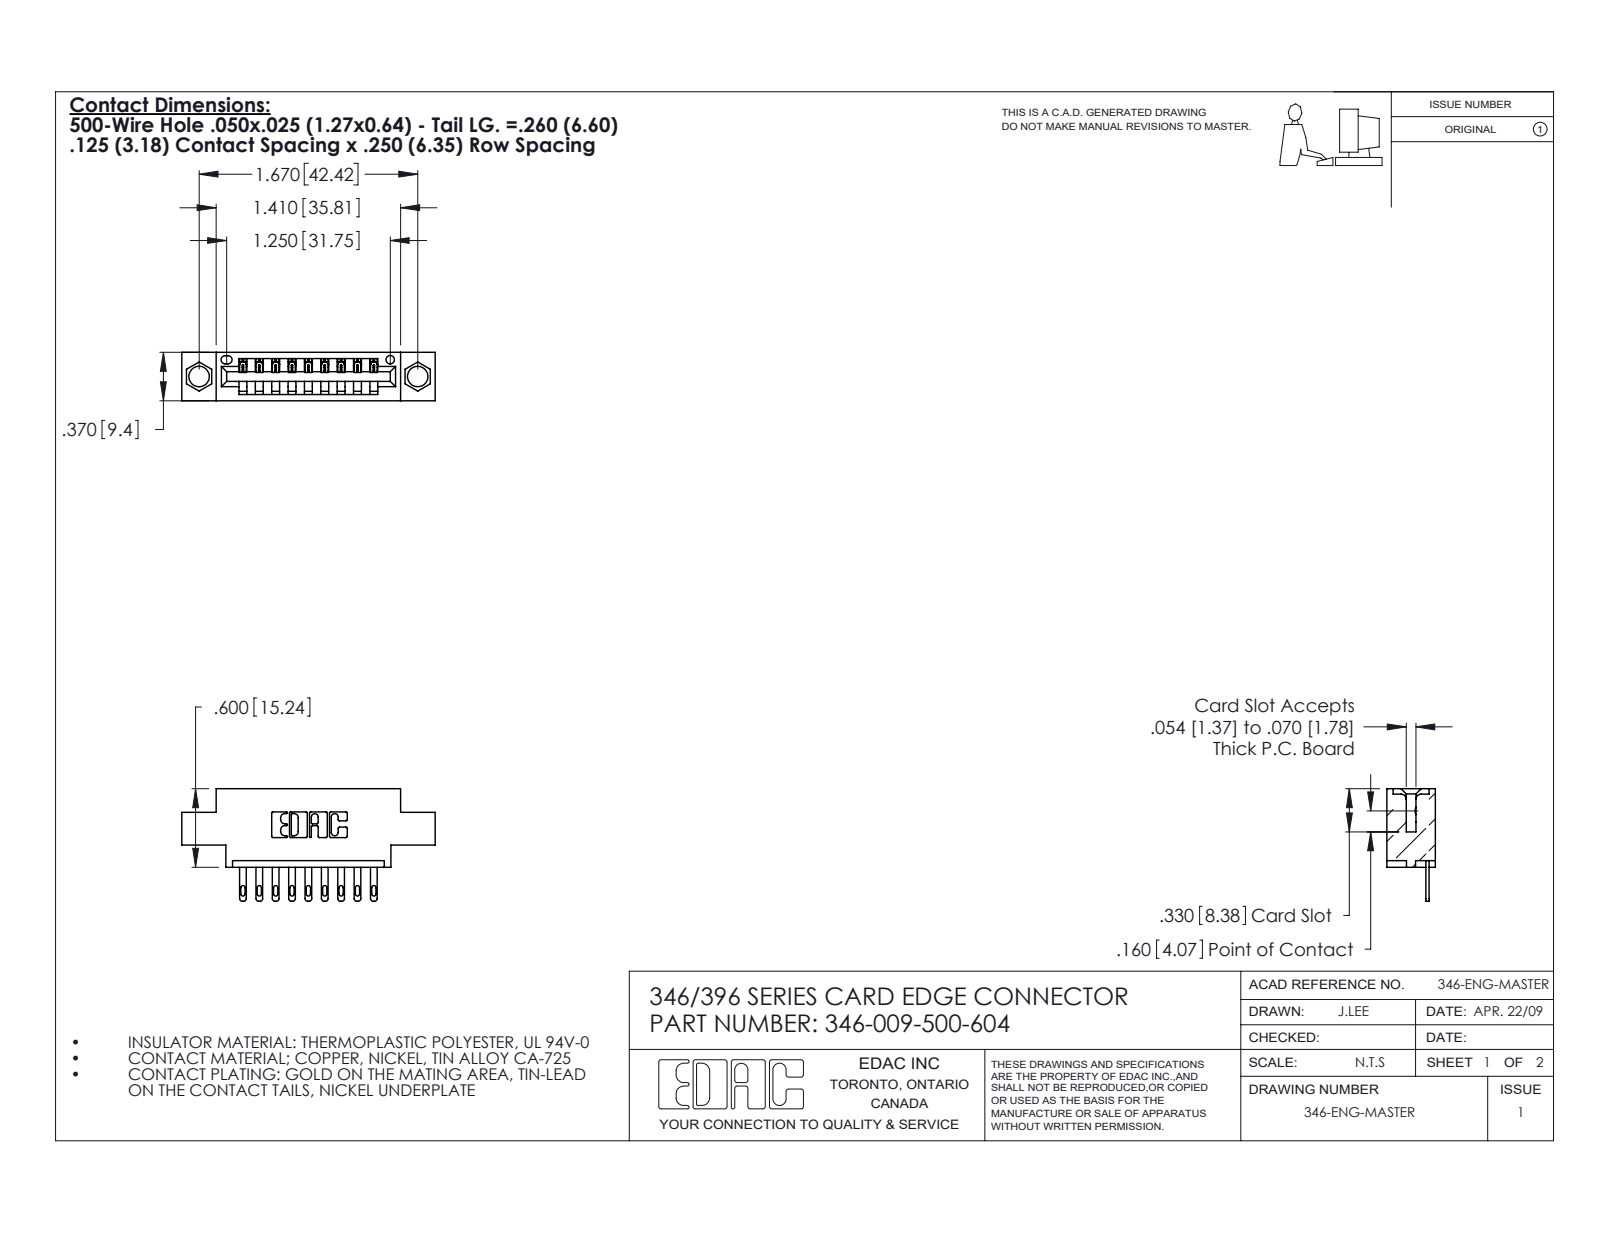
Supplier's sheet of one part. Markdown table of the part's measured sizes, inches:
| quantity | value |
| --- | --- |
| part name | 346-009-500-604; 346 Part_0.170 Offset - 0.156 Dia-TH; 345-292-001_345-293-100 |
| STEP written by | SolidWorks 2020 (CONFIG_CONTROL_DESIGN) |
| units | inches |
| bodies | 10 solids, 626 faces (400 planar, 226 cylindrical, 0 other) |
| overall size | 1.935 × 0.86 × 0.37 |
| volume | 0.258 in³ |
| surface area | 7.657 in² |
| round holes (diameter × count) | 0.156 × 2, 0.064 × 1 |
| partial cylindrical surfaces (radius × count) | 0.01 × 22, 0.006 × 18, 0.016 × 18, 0.02 × 18, 0.007 × 6, 0.031 × 6, 0.026 × 3, 0.031 × 2 |
| main face-to-face distances | 0.25, 0.37, 0.048, 0.322, 0.072, 0.298, 0.025, 0.222, 0.148, 0.1 |
| hole center spacings | 0.246, 1.465, 1.67 |
